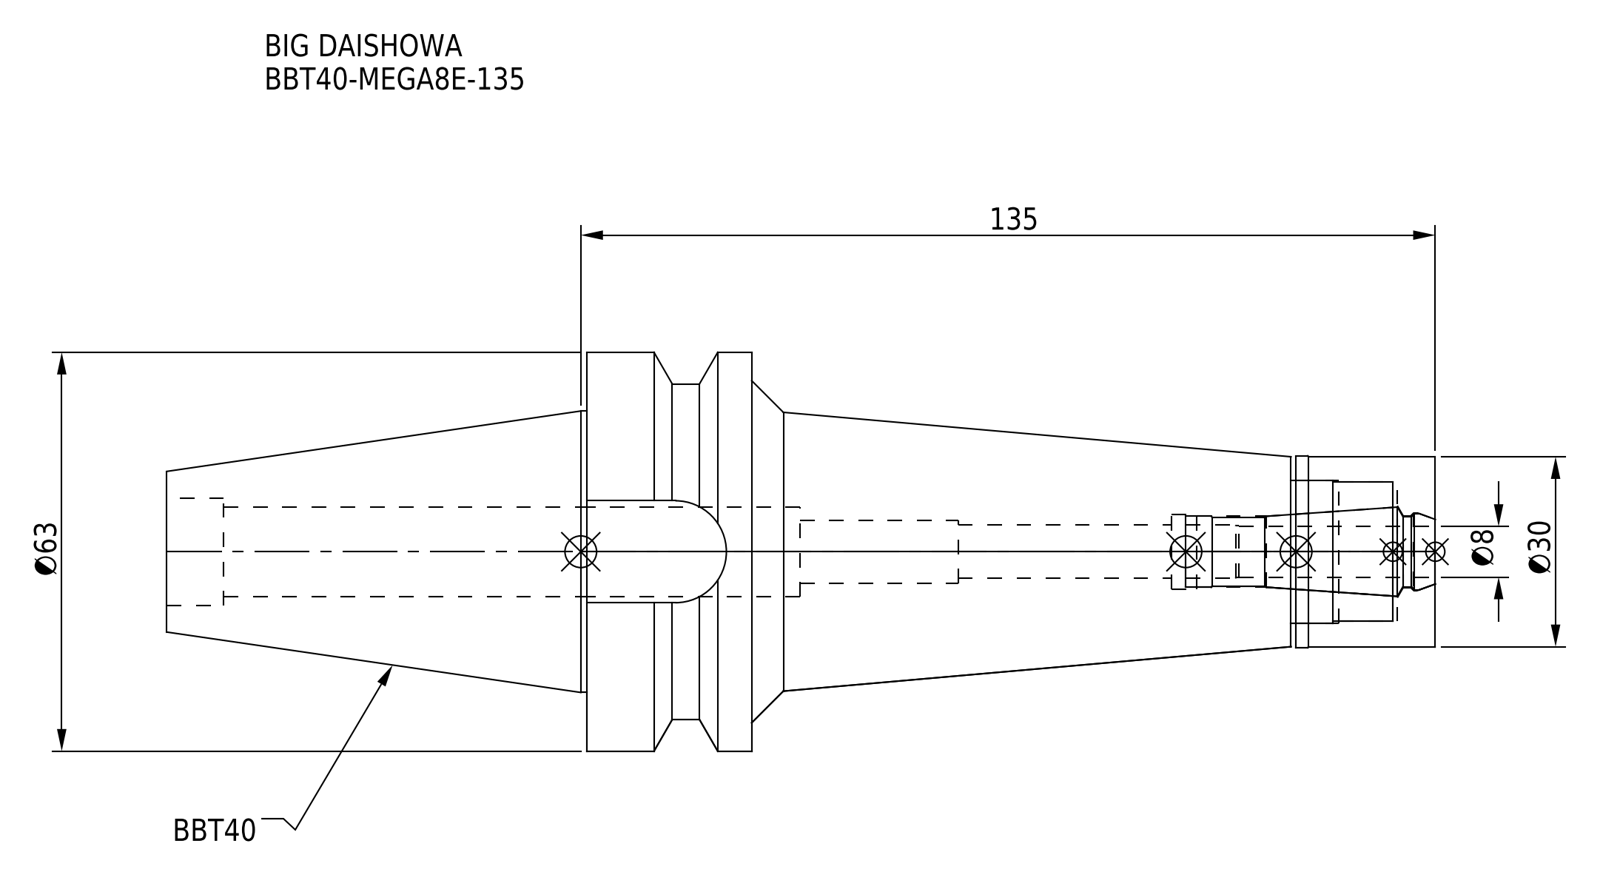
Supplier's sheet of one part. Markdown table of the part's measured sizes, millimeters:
| quantity | value |
| --- | --- |
| part name | BBT40-MEGA8E-135; BBT40-MEGA8E-135-080-FreeParts; BBT40ME08135-080_ASM.stp; BBT40-MEGA8E-135_1.stp (+3 more) |
| STEP written by | SolidWorks 2019 (CONFIG_CONTROL_DESIGN) |
| units | millimeters |
| bodies | 2 solids, 81 faces (21 planar, 40 cylindrical, 20 other) |
| overall size | 200.4 × 63 × 63 |
| volume | 223 053 mm³ |
| surface area | 40 848 mm² |
| round holes (diameter × count) | 8.4 × 1, 10 × 1, 11.2 × 1, 11.4 × 1, 11.8 × 1, 12.3 × 1, 14.2 × 1, 17 × 1, 22 × 1, 22.5 × 1 |
| round bosses / shafts (diameter × count) | 63 × 1, 53 × 1, 44.45 × 1, 30.3 × 1, 30 × 1 |
| partial cylindrical surfaces (radius × count) | 8.05 × 1 |
| main face-to-face distances | 26, 108, 134, 16.1, 85.2, 45, 22, 86, 112, 22.8 |
